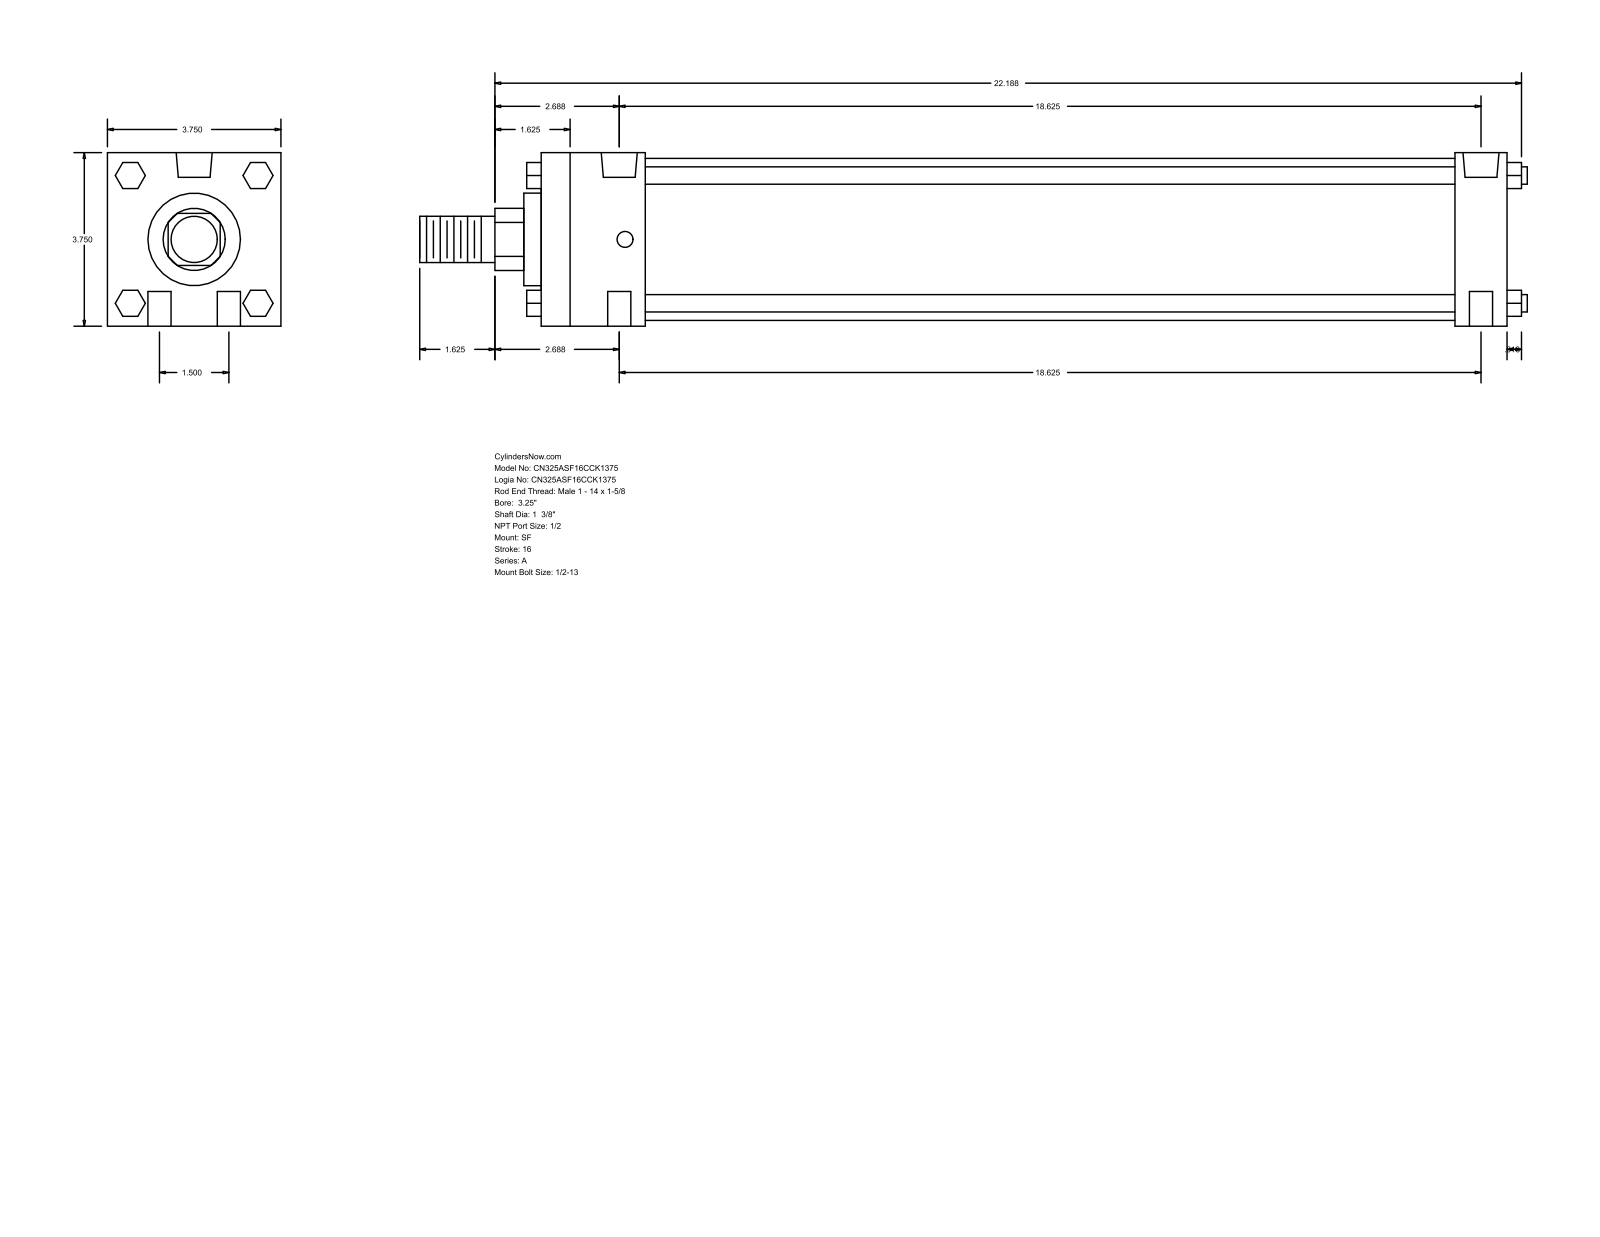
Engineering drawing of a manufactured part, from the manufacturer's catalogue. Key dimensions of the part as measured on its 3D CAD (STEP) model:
Part name (STEP PRODUCT): A_SF__0325_1.375
STEP written by: GSSL Pune (CONFIG_CONTROL_DESIGN)
Units: millimetres
Bodies: 0 solids, 124 faces (94 planar, 30 cylindrical, 0 other)
Overall size (bounding box): 608.01 × 95.25 × 95.25
Round holes (diameter × count): ⌀12.7 ×4, ⌀8.73 ×2, ⌀19.77 ×2
Round bosses / shafts (diameter × count): ⌀9.53 ×4, ⌀88.9 ×1, ⌀50.8 ×1, ⌀34.92 ×1, ⌀25.4 ×1
Partial cylindrical surfaces — rounded edges, fillets, slot ends (radius × count): R17.06 ×1
Main face-to-face distances: 95.24, 530.22, 57.15, 501.65, 28.57, 444.5, 473.07, 66.67, 9.52, 511.17
Hole centre spacings: 19.05, 473.46, 473.08, 38.1, 474.61, 466.72
